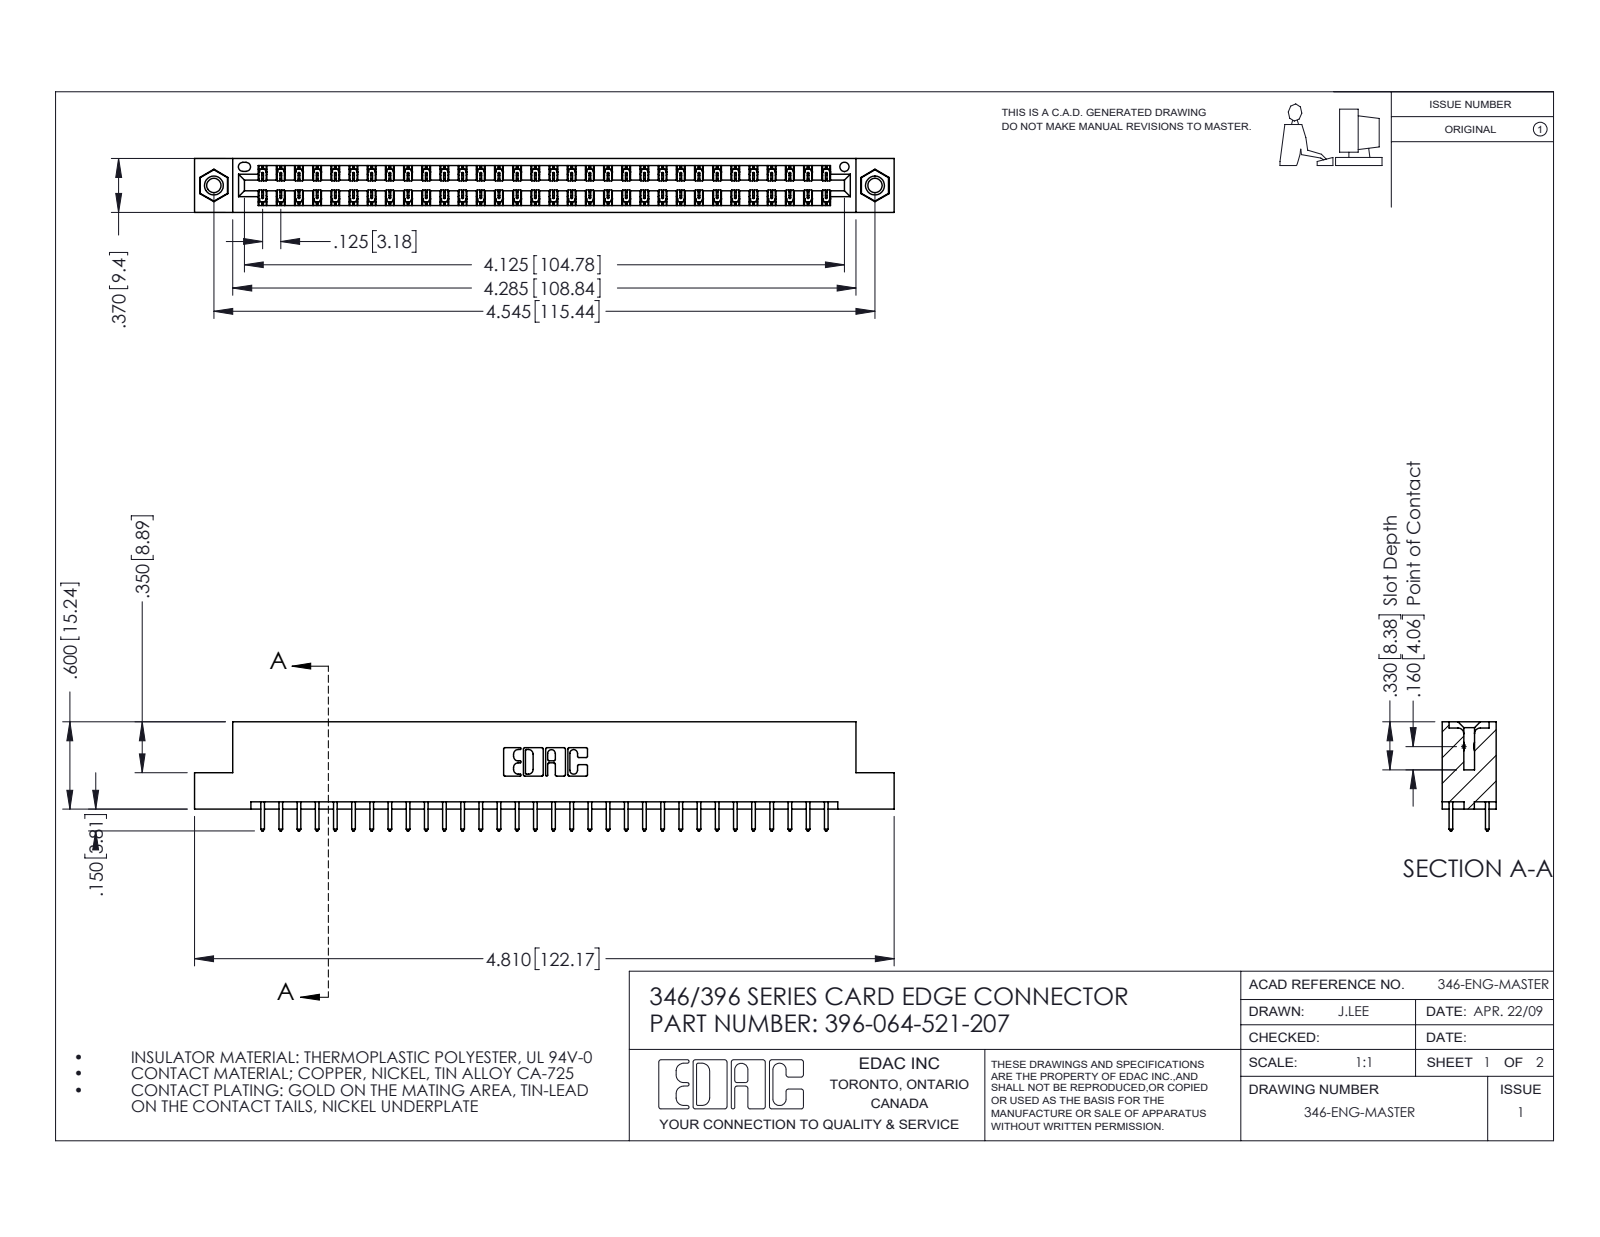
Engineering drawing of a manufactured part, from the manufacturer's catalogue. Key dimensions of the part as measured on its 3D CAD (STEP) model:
Part name (STEP PRODUCT): 346 Part_Flush Mounting Lugs - 0.156 Dia-TI; 345-250-001_345-250-005-103; 345-292-001_345-293-121; 396-064-521-207
STEP written by: SolidWorks 2016 (CONFIG_CONTROL_DESIGN)
Units: inches
Bodies: 67 solids, 3510 faces (2348 planar, 1146 cylindrical, 16 other)
Overall size (bounding box): 4.81 × 0.75 × 0.37
Volume: 0.72 in³ · Surface area: 24.67 in²
Round holes (diameter × count): ⌀0.098 ×2, ⌀0.125 ×2, ⌀0.156 ×2, ⌀0.064 ×1
Round bosses / shafts (diameter × count): ⌀0.155 ×2
Partial cylindrical surfaces — rounded edges, fillets, slot ends (radius × count): R0.006 ×96, R0.01 ×64, R0.01 ×22, R0.007 ×6, R0.031 ×6, R0.026 ×3, R0.014 ×2, R0.022 ×2
Main face-to-face distances: 0.048, 0.322, 0.25, 0.37, 0.072, 0.298, 0.025, 0.275, 0.148, 0.222
Hole centre spacings: 0.246, 4.337, 4.545
